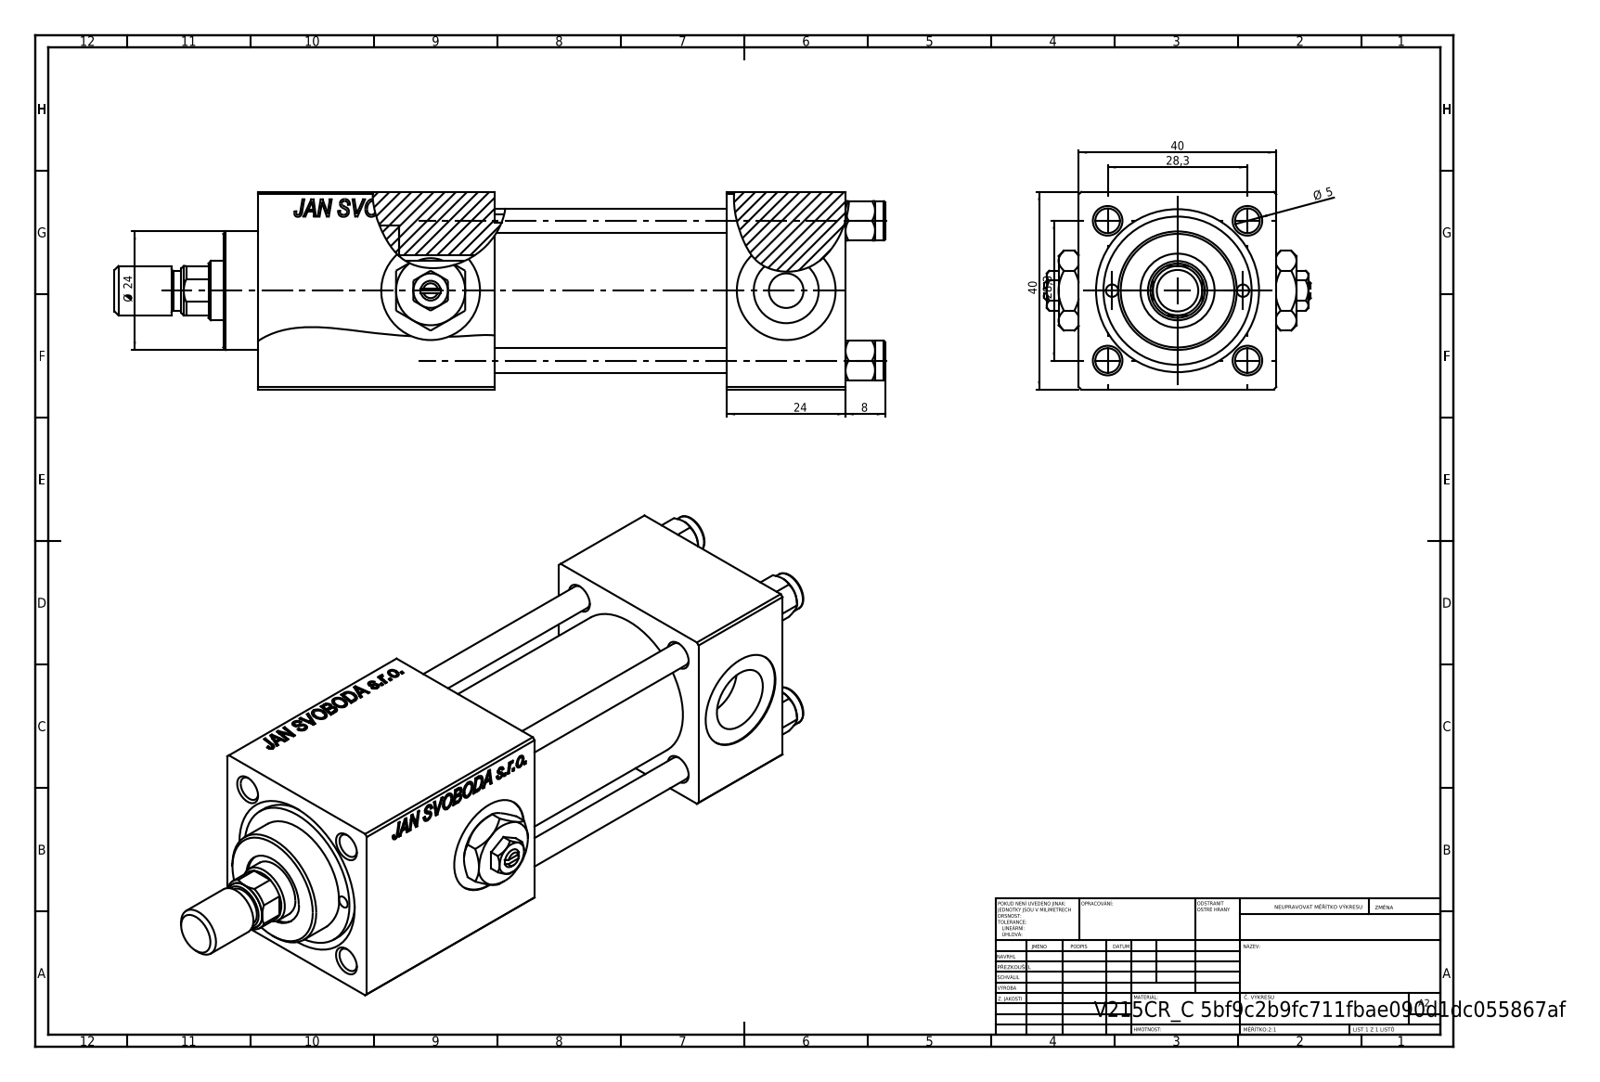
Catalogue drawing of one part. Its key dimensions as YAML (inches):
part_name: "V215_VC_A; NUT_M5_C; ROD_END_AH; V215CR_C_Body (+3 more)"
step_written_by: "SolidWorks 2019 (CONFIG_CONTROL_DESIGN)"
units: inches
bodies: {solids: 14, faces: 1268, planar: 578, cylindrical: 106, other: 584}
overall_size: [6.142, 2.126, 1.575]
volume: 8.663
surface_area: 88.19
round_holes:
  - {diameter: 0.197, count: 4}
  - {diameter: 0.787, count: 3}
  - {diameter: 0.098, count: 2}
  - {diameter: 0.276, count: 2}
  - {diameter: 0.518, count: 2}
  - {diameter: 0.256, count: 1}
  - {diameter: 0.472, count: 1}
  - {diameter: 0.591, count: 1}
  - {diameter: 0.984, count: 1}
  - {diameter: 1.181, count: 1}
round_bosses_or_shafts:
  - {diameter: 0.315, count: 5}
  - {diameter: 1.22, count: 1}
  - {diameter: 0.945, count: 1}
  - {diameter: 0.394, count: 1}
partial_cylinders:
  - {radius: 0.217, count: 1}
face_to_face_distances: [1.575, 0.945, 1.567, 1.89, 3.555, 2.61, 2.795, 1.85, 0.76, 3.74]
hole_center_spacings: [0.558, 0.788, 1.114, 1.214, 0.522, 1.576, 1.043, 2.835]
